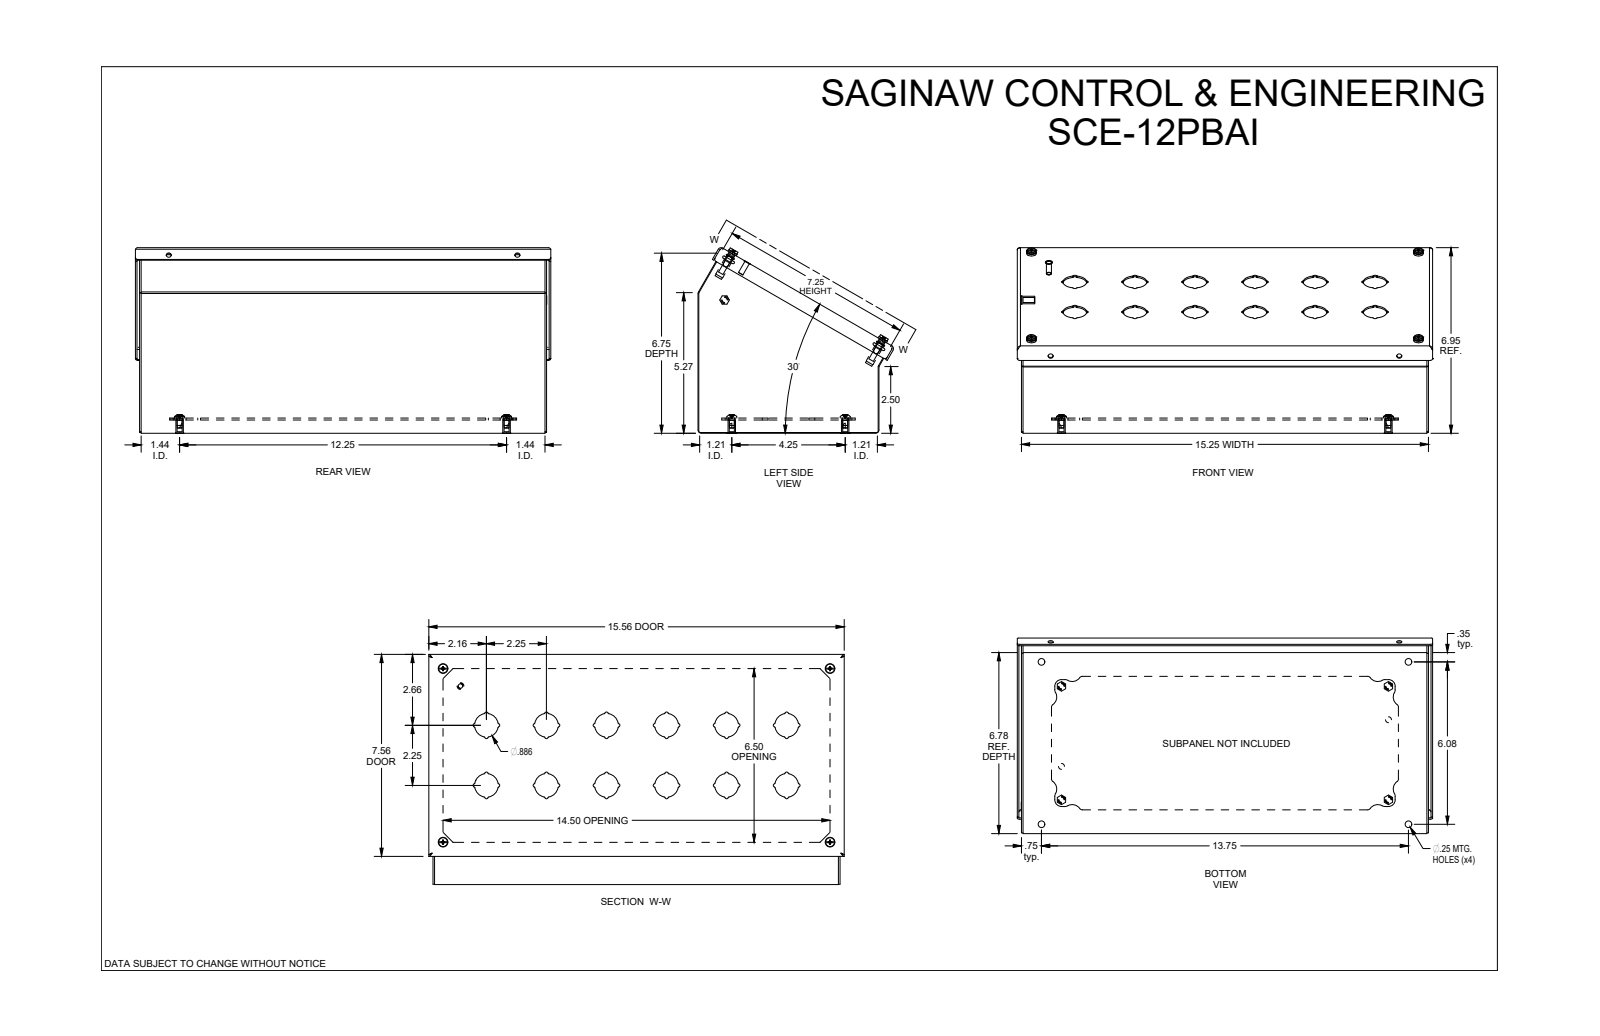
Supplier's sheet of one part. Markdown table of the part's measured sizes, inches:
| quantity | value |
| --- | --- |
| part name | SCE-12PBAI |
| STEP written by | SolidWorks 2019 (AUTOMOTIVE_DESIGN) |
| units | inches |
| bodies | 28 solids, 998 faces (341 planar, 399 cylindrical, 258 other) |
| overall size | 15.563 × 7.345 × 6.978 |
| volume | 34.35 in³ |
| surface area | 1 125 in² |
| round holes (diameter × count) | 0.25 × 12, 0.19 × 9, 0.22 × 4, 0.266 × 4, 0.281 × 4, 0.317 × 4, 0.187 × 2, 0.218 × 2, 0.193 × 1 |
| round bosses / shafts (diameter × count) | 0.188 × 9, 0.28 × 5, 0.373 × 4, 0.362 × 4, 0.34 × 4, 0.334 × 4, 0.292 × 4, 0.27 × 4 |
| partial cylindrical surfaces (radius × count) | 0.04 × 100, 0.062 × 48, 0.06 × 20, 0.03 × 12, 0.25 × 12, 0.443 × 12, 0.01 × 10, 0.115 × 8 |
| main face-to-face distances | 0.06, 0.06, 6.72, 15.19, 0.511, 0.571, 0.436, 0.075, 0.496, 6.66 |
| hole center spacings | 14.5, 1.183, 5.219, 13.032, 13.988, 1.25, 2.292, 3 |
